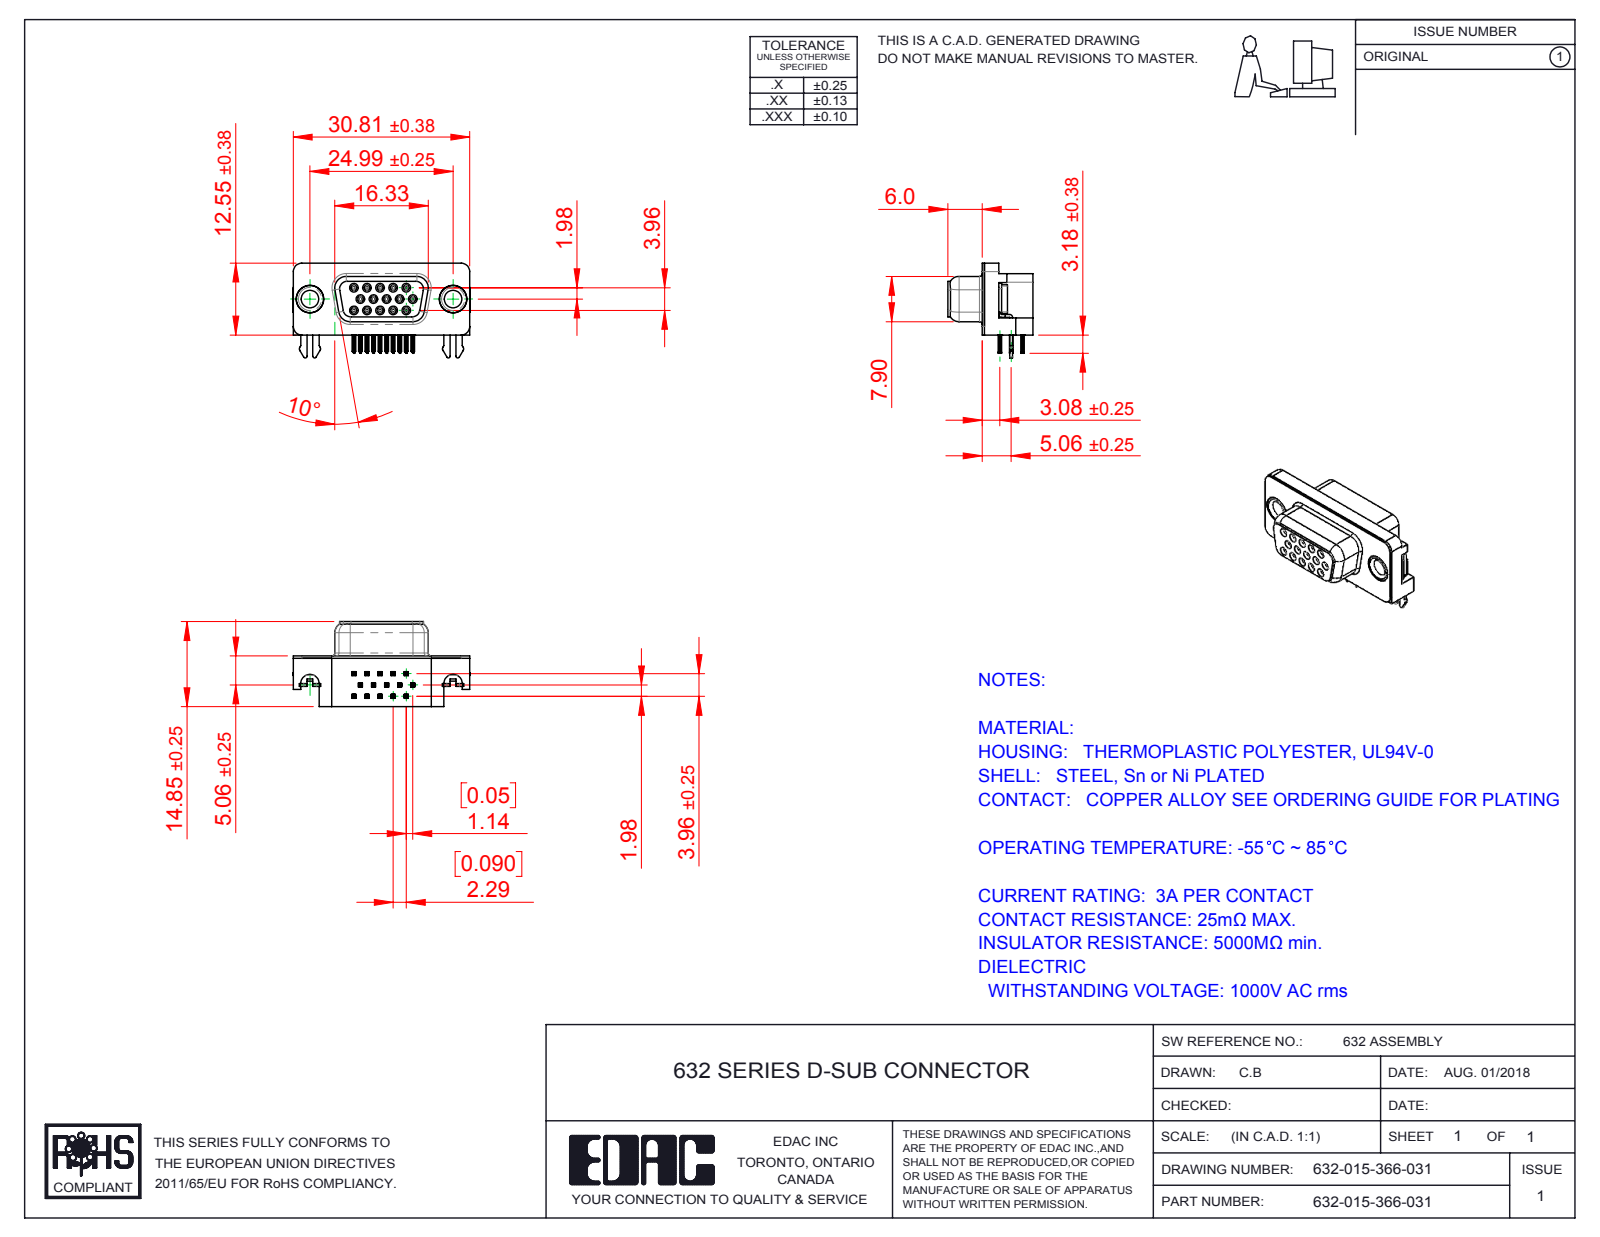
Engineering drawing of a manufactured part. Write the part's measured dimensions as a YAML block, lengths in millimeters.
part_name: "632 Housing_15 Socket; 632 2 Prong Board Lock; 632 Contact Bottom; 632 Thru Hole Rivet (+4 more)"
step_written_by: "SolidWorks 2016 (CONFIG_CONTROL_DESIGN)"
units: millimeters
bodies: {solids: 21, faces: 2298, planar: 990, cylindrical: 594, other: 714}
overall_size: [30.89, 16.55, 14.85]
volume: 2908
surface_area: 4994
round_holes:
  - {diameter: 0.8, count: 15}
  - {diameter: 0.9, count: 15}
  - {diameter: 3.05, count: 2}
  - {diameter: 4, count: 2}
  - {diameter: 4.8, count: 2}
  - {diameter: 5, count: 2}
round_bosses_or_shafts:
  - {diameter: 1.2, count: 15}
  - {diameter: 4.9, count: 2}
  - {diameter: 4.75, count: 2}
  - {diameter: 3.85, count: 2}
partial_cylinders:
  - {radius: 0.1, count: 120}
  - {radius: 0.15, count: 60}
  - {radius: 0.35, count: 30}
  - {radius: 0.34, count: 15}
  - {radius: 1, count: 11}
  - {radius: 0.28, count: 10}
  - {radius: 0.5, count: 10}
  - {radius: 0.25, count: 8}
face_to_face_distances: [0.4, 1.98, 8.45, 8.85, 2.9, 2.5, 5.95, 6.4, 6.7, 7.05]
hole_center_spacings: [2.28, 2.29, 3.96, 4.57, 6.05, 3.97, 4.58, 6.86]
